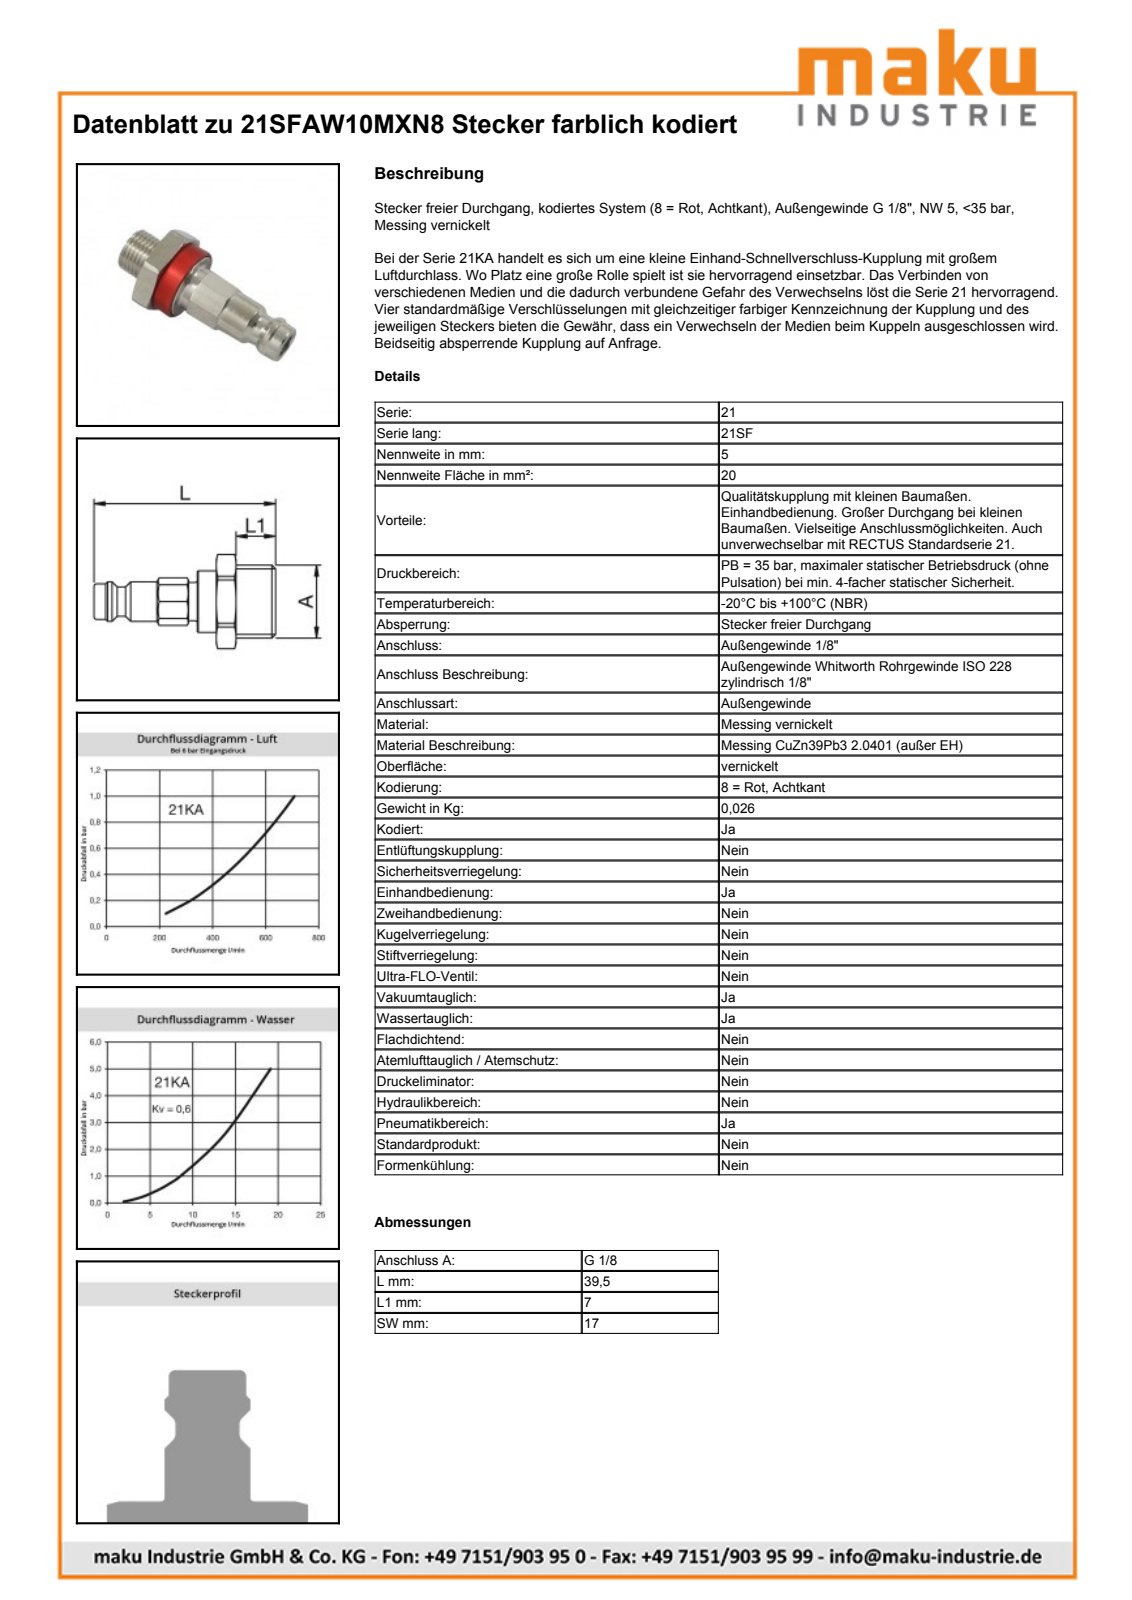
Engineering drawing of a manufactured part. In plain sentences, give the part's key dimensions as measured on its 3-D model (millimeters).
The part is named "D110097; D110095; D103012". Its 3-D file was written by "Autodesk Inventor 2013 (AUTOMOTIVE_DESIGN)". It is 2 solids with 65 faces: 21 planar, 17 cylindrical and 27 other. Overall it measures 39.5 by 19 by 17 millimeters. Its volume is 3 205 cubic millimeters and its surface area 2 840 square millimeters. Round holes: 1 of diameter 4.95, 1 of diameter 13.85, 1 of diameter 14.05. Round bosses or shafts: 1 of diameter 15.5, 1 of diameter 14, 1 of diameter 9.73, 1 of diameter 9.7, 1 of diameter 9, 1 of diameter 8.1, 1 of diameter 6.65. Partial cylindrical surfaces (rounded edges, fillets, slot ends): 1 of radius 9.5. The main face-to-face distances are 4.5, 10, 17, 3.5, 13.5, 9, 4.2, 8.7, 23.5, 23.8.
